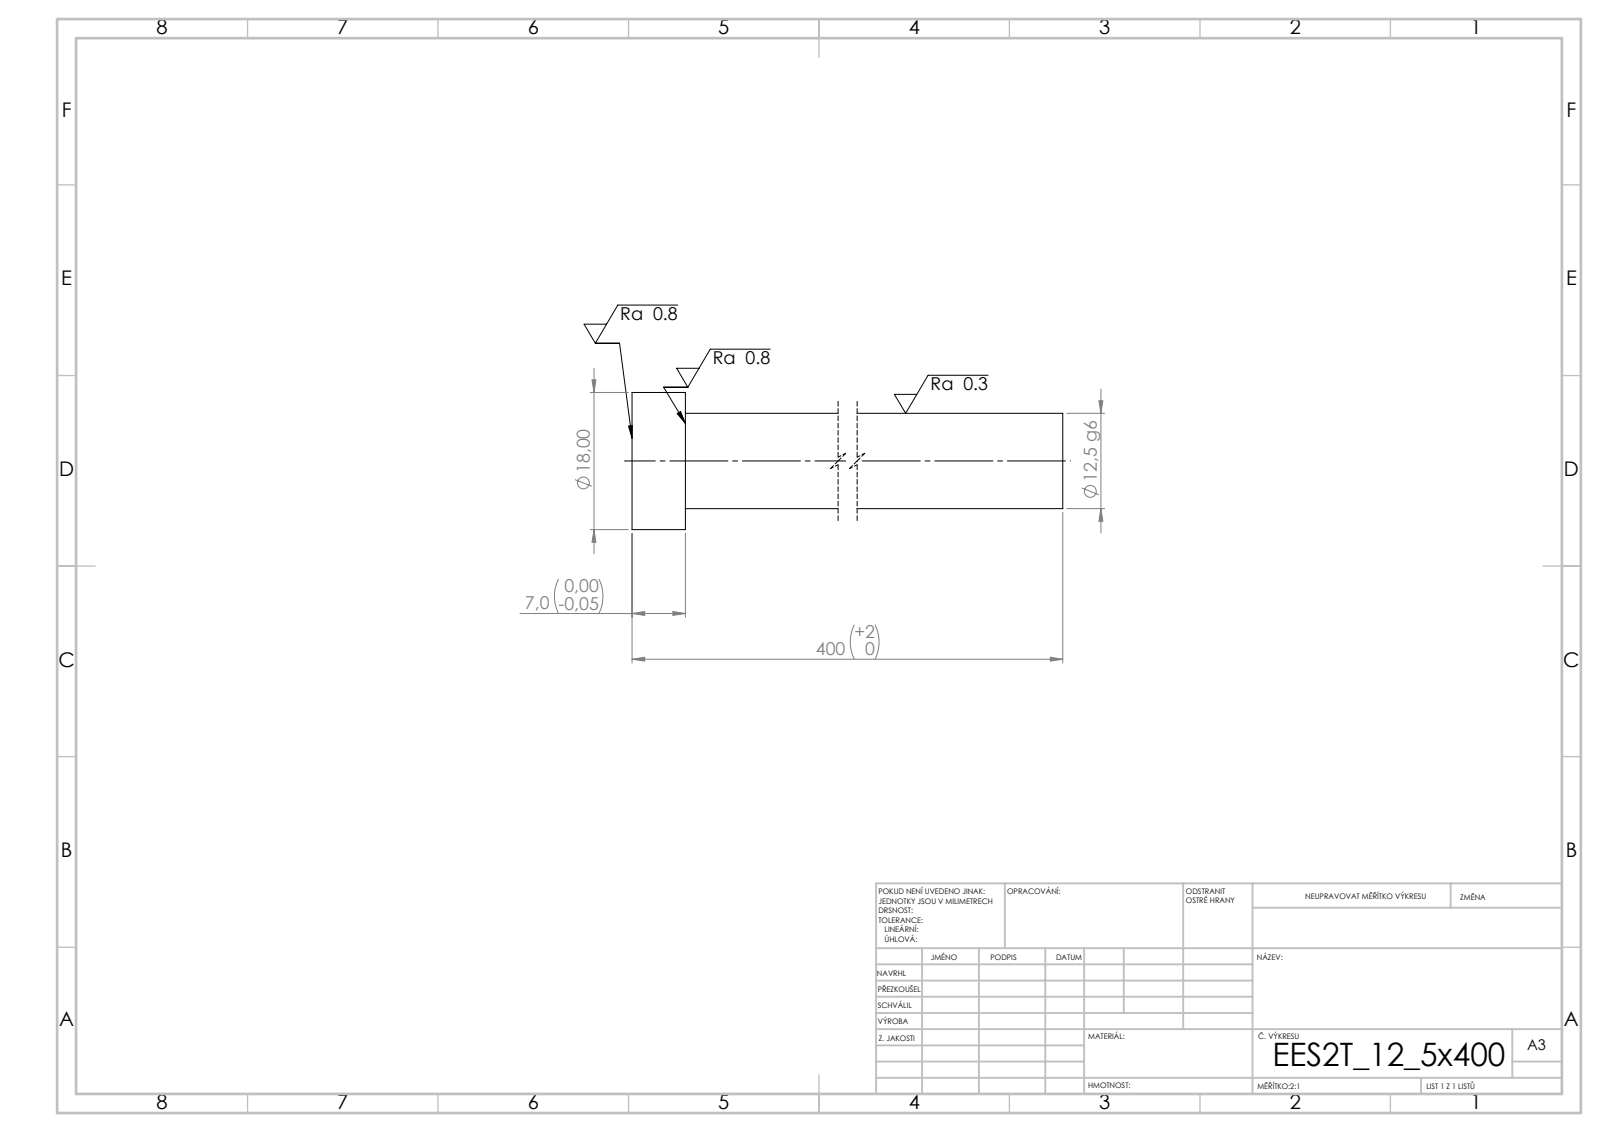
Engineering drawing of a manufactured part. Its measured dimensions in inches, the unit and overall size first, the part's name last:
Units: inches
Overall size (bounding box): 15.748 × 0.709 × 0.709
Round bosses / shafts (diameter × count): ⌀0.709 ×1, ⌀0.492 ×1
Main face-to-face distances: 0.276, 15.748, 15.472
Volume: 3.052 in³ · Surface area: 25.32 in²
Bodies: 1 solid, 7 faces (3 planar, 4 cylindrical, 0 other)
STEP written by: SolidWorks 2019 (CONFIG_CONTROL_DESIGN)
